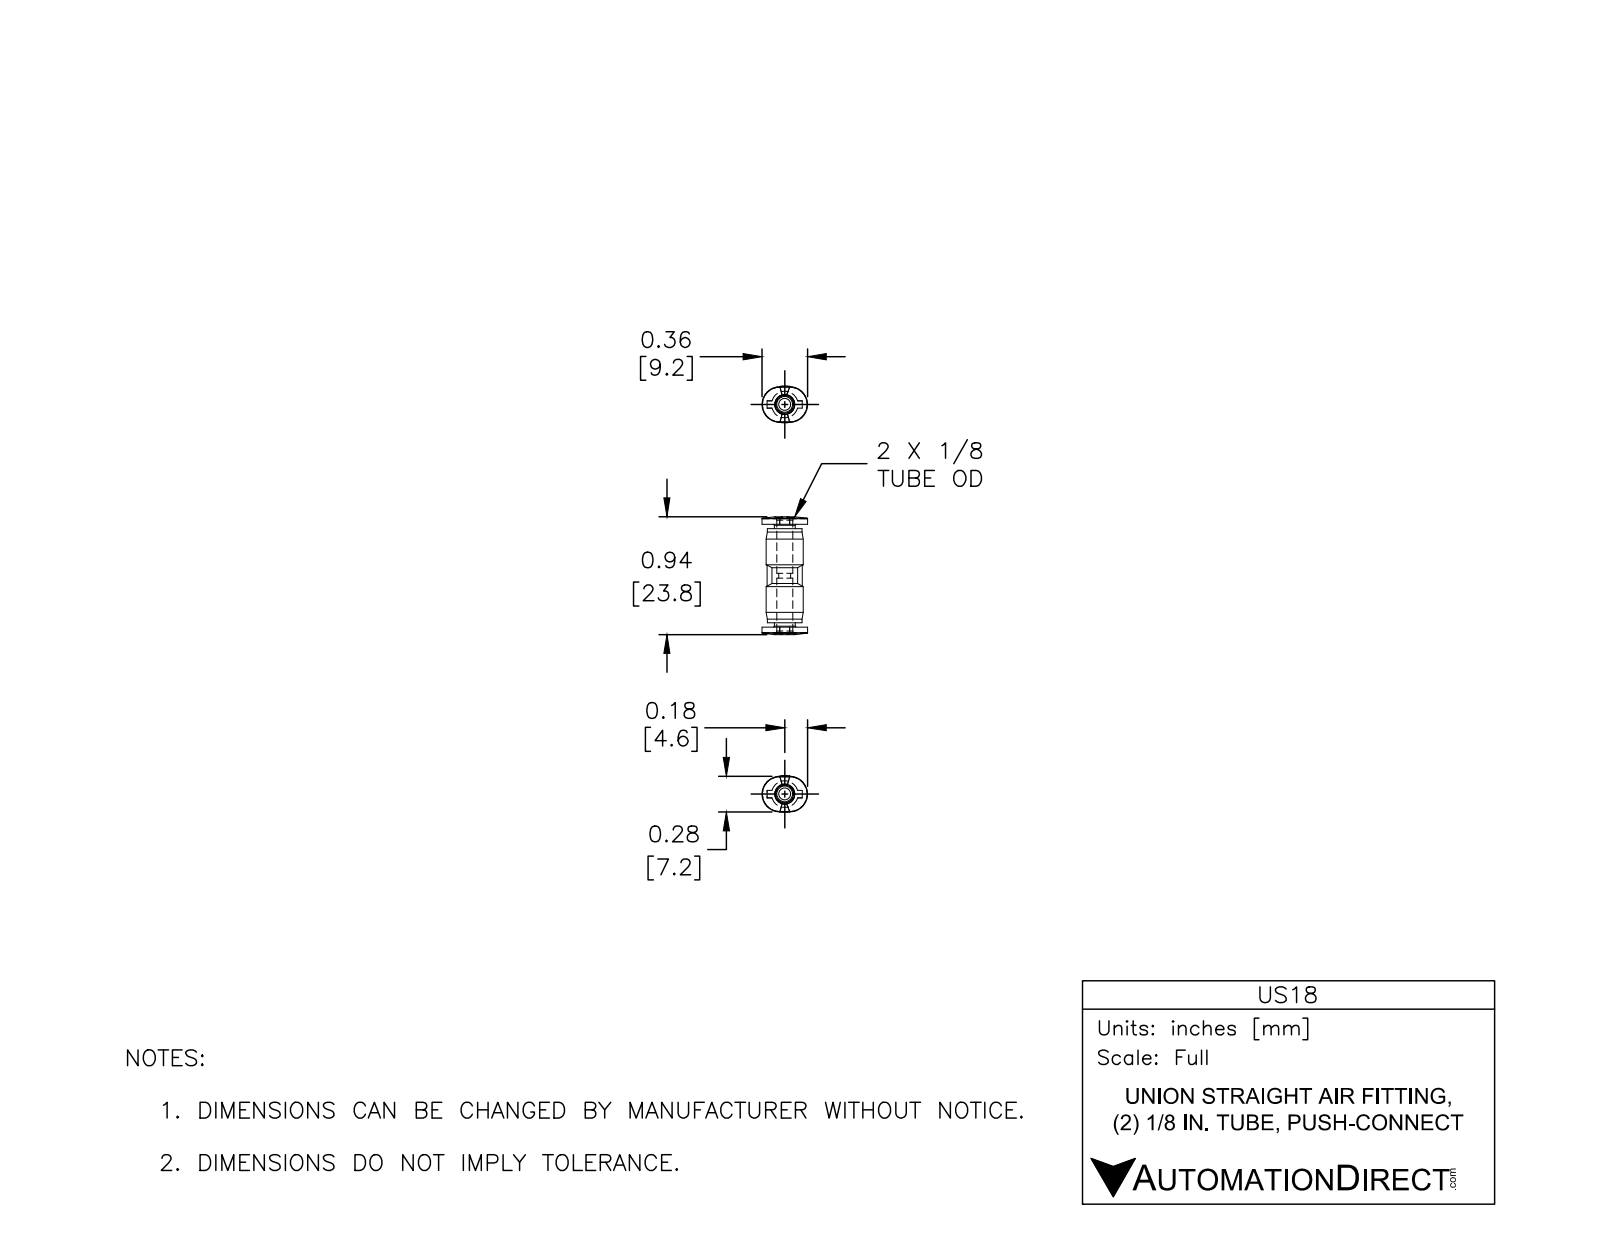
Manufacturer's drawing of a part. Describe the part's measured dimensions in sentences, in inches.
The part is named "US18". Its 3-D file was written by "SolidWorks 2015 (CONFIG_CONTROL_DESIGN)". It is 1 solid with 87 faces: 18 planar, 25 cylindrical and 44 other. Overall it measures 0.937 by 0.362 by 0.295 inches. Its volume is 0.045 cubic inches and its surface area 1.558 square inches. Round holes: 1 of diameter 0.094, 1 of diameter 0.126. Round bosses or shafts: 1 of diameter 0.295, 1 of diameter 0.276, 1 of diameter 0.213, 1 of diameter 0.165. Partial cylindrical surfaces (rounded edges, fillets, slot ends): 2 of radius 0.142. The main face-to-face distances are 0.035, 0.783, 0.819, 0.748, 0.112, 0.171, 0.059, 0.39, 0.429, 0.354.
